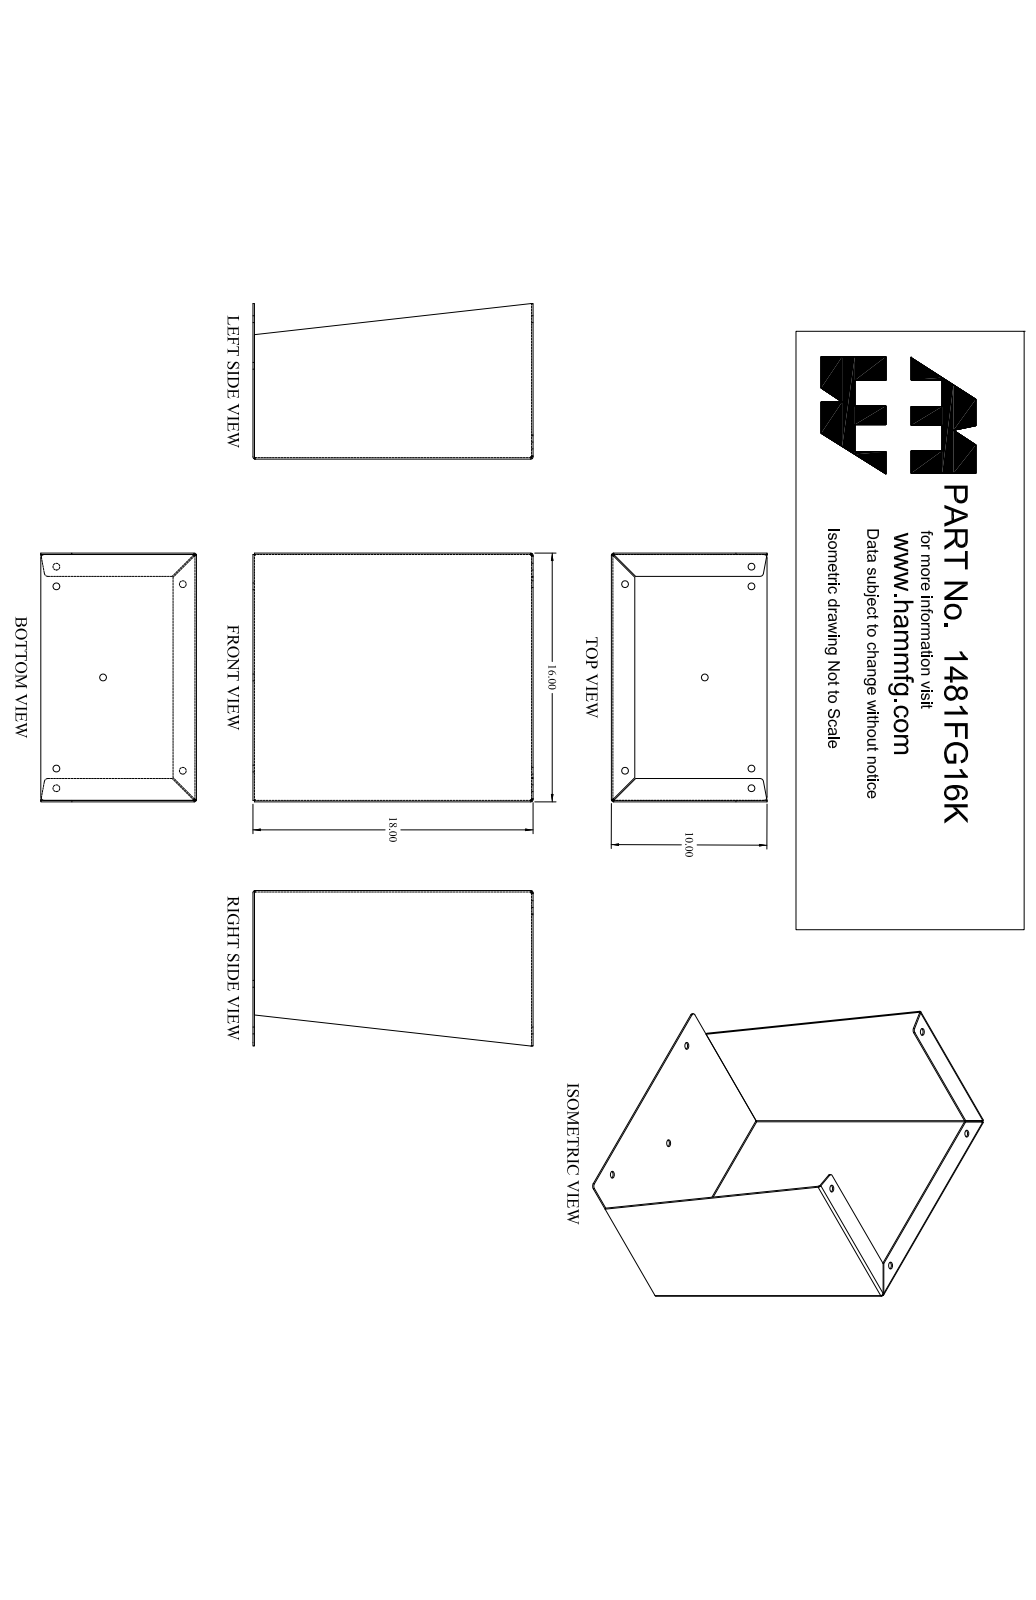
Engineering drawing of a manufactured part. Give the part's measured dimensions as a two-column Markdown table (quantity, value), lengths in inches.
| quantity | value |
| --- | --- |
| part name | 1481FG16K_Default |
| STEP written by | SolidWorks 2019 (CONFIG_CONTROL_DESIGN) |
| units | inches |
| bodies | 1 solid, 78 faces (42 planar, 30 cylindrical, 6 other) |
| overall size | 18 × 16 × 10 |
| volume | 76.43 in³ |
| surface area | 1 622 in² |
| round holes (diameter × count) | 0.437 × 7 |
| partial cylindrical surfaces (radius × count) | 0.048 × 6, 0.143 × 6, 0.22 × 4 |
| main face-to-face distances | 0.095, 15.905, 15.81, 16, 0.095, 17.81, 17.905, 17.905, 18, 1.405 |
| hole center spacings | 6.582, 7.891, 8.126, 8.202, 14.375, 1.266, 1.266, 7.731 |
